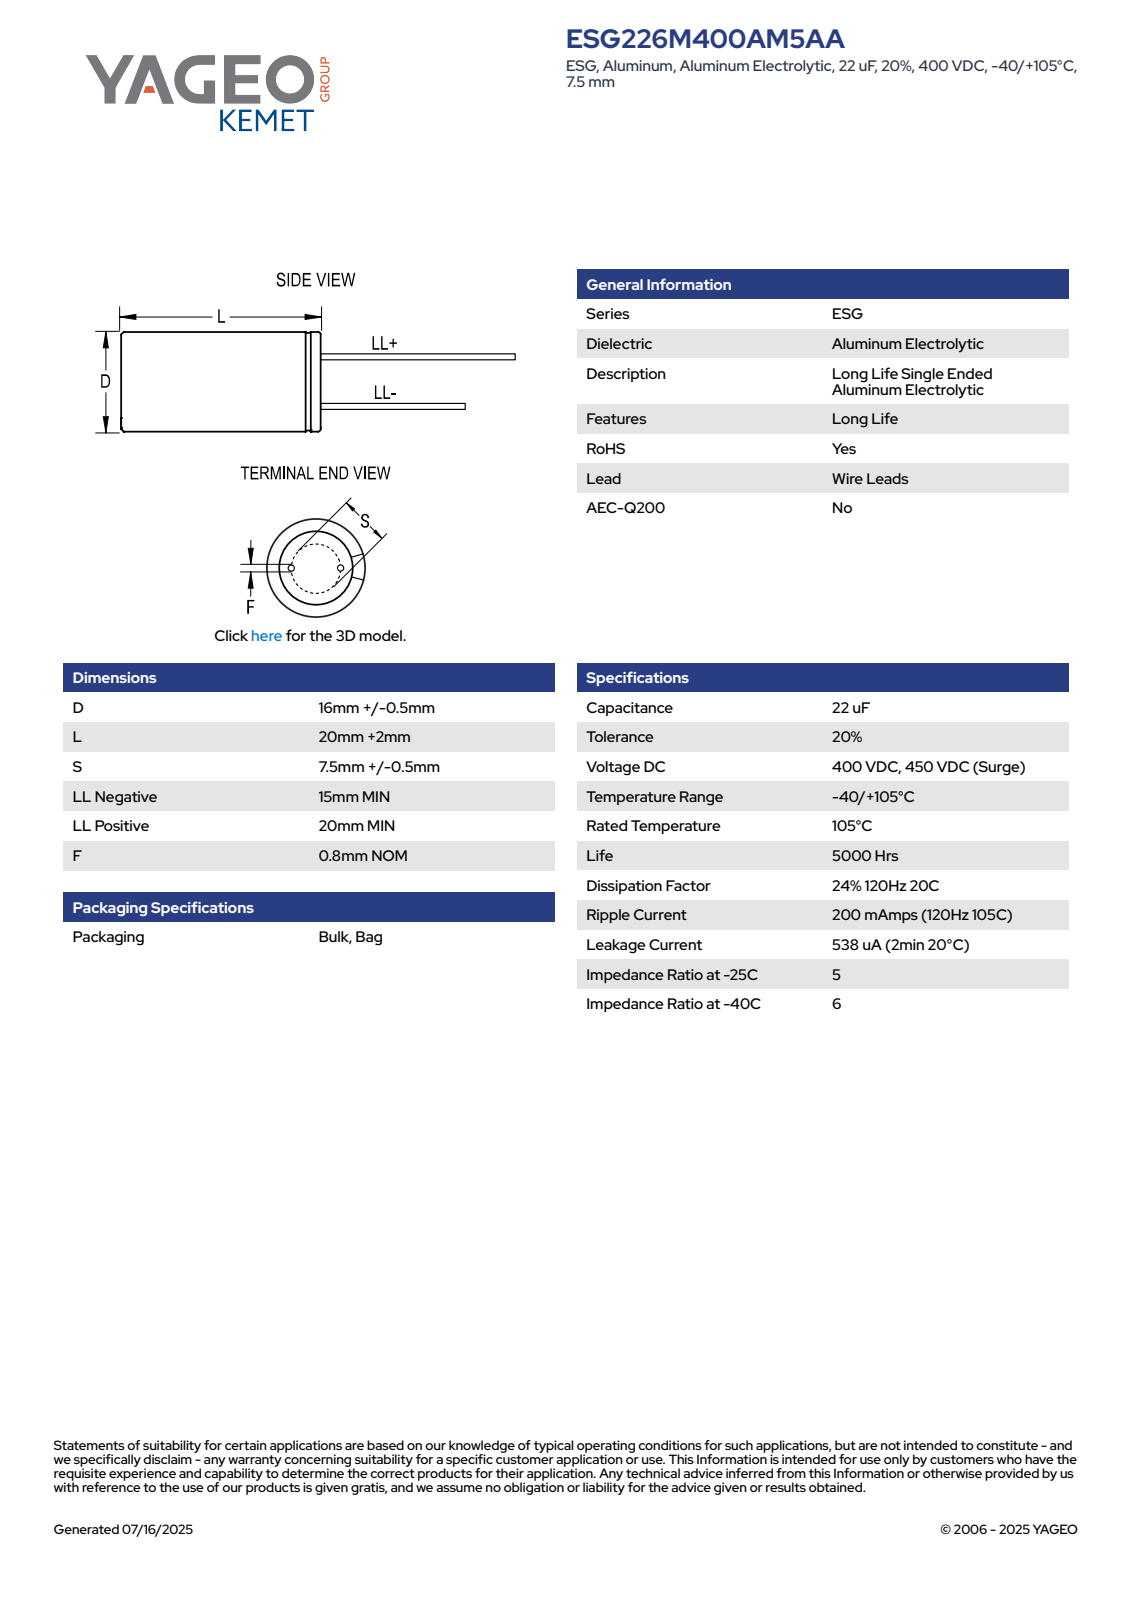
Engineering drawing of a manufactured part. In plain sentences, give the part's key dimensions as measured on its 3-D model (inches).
The part is named "CAR_KLP_16X20_D16.5L22S7.5F0.8". Its 3-D file was written by "SolidWorks 2014 (AUTOMOTIVE_DESIGN)". It is 4 solids with 75 faces: 61 planar, 8 cylindrical and 6 other. Overall it measures 1.654 by 0.65 by 0.65 inches. Its volume is 0.285 cubic inches and its surface area 2.664 square inches. Round bosses or shafts: 2 of diameter 0.031, 1 of diameter 0.65. The main face-to-face distances are 0.866, 0.867, 0.197, 1.457, 1.654, 1.457, 1.654, 0.591, 0.787, 0.087.
